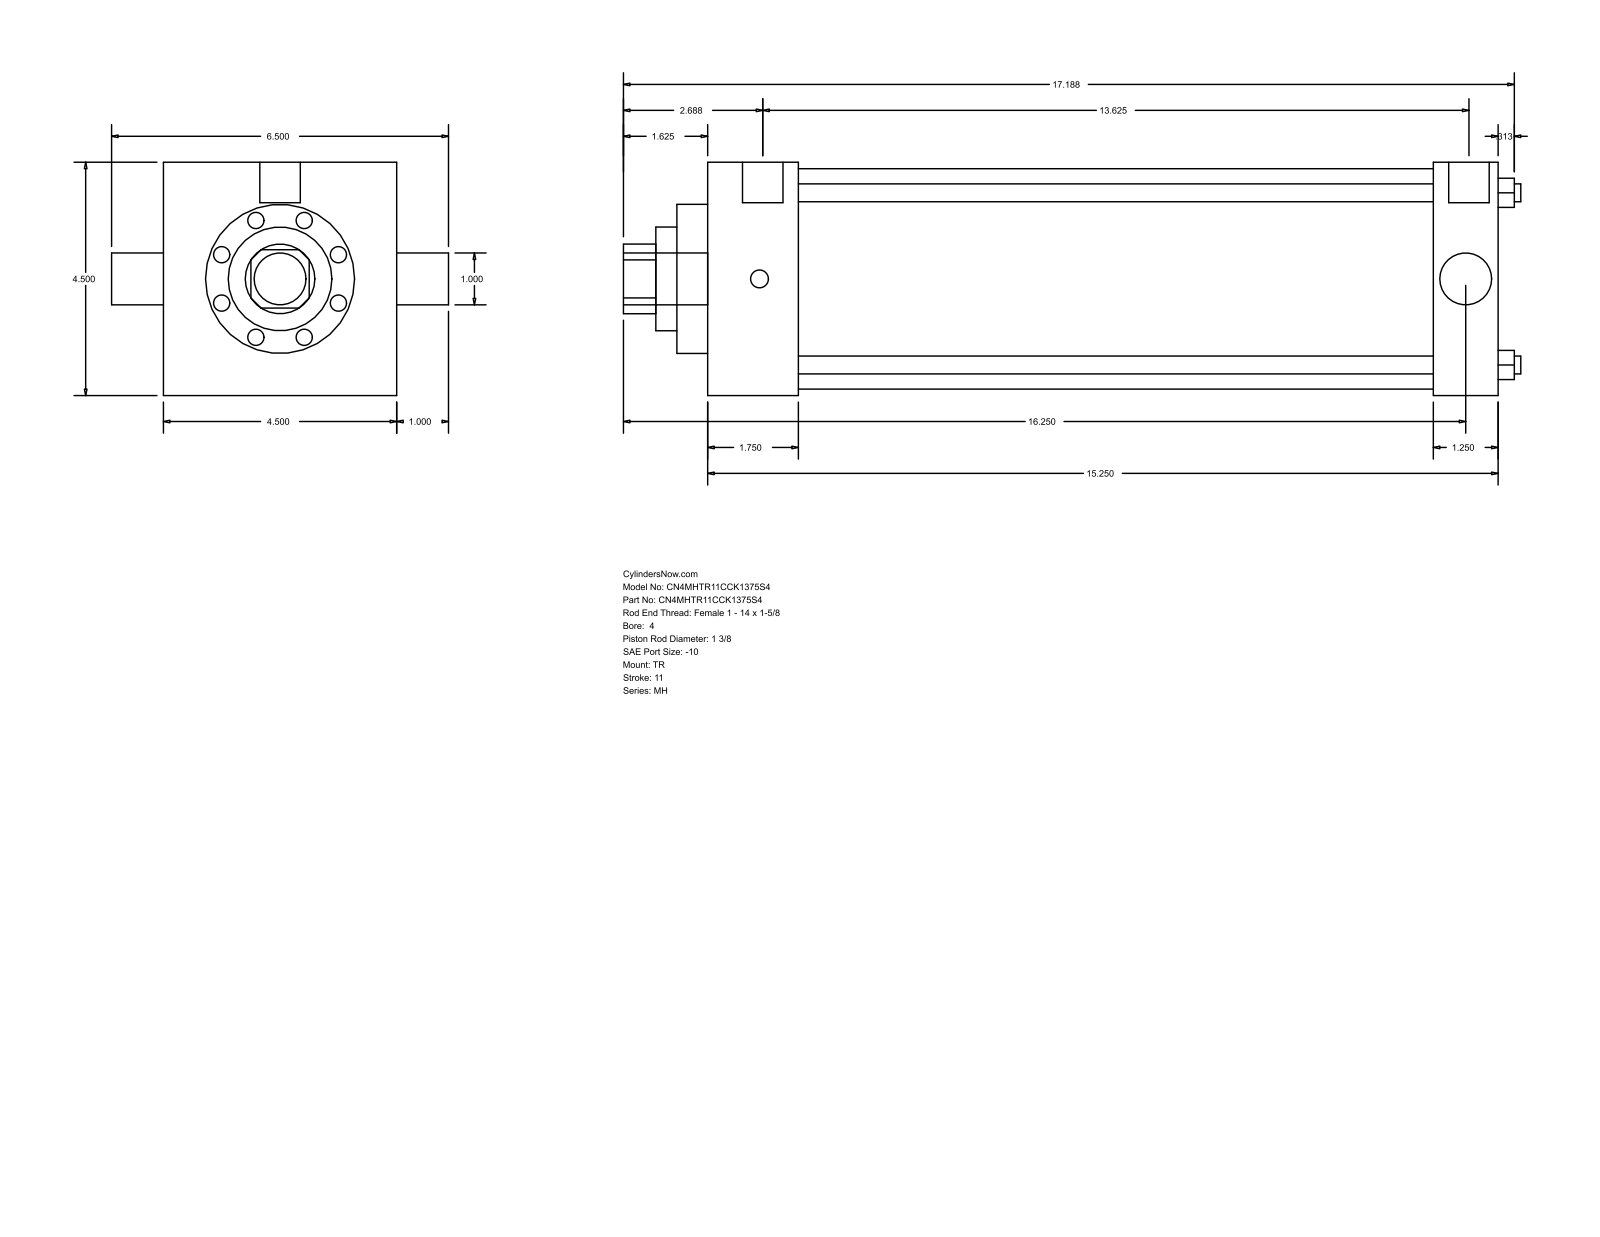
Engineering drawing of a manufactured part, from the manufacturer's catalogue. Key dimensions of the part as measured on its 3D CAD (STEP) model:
Part name (STEP PRODUCT): MH_TR__0400_1.375
STEP written by: GSSL Pune (CONFIG_CONTROL_DESIGN)
Units: millimetres
Bodies: 0 solids, 86 faces (61 planar, 25 cylindrical, 0 other)
Overall size (bounding box): 439.74 × 165.1 × 114.3
Round holes (diameter × count): ⌀8.76 ×4, ⌀25.4 ×1, ⌀34.92 ×1, ⌀50.8 ×1, ⌀73.03 ×1, ⌀107.95 ×1
Round bosses / shafts (diameter × count): ⌀8.73 ×3, ⌀19.84 ×2, ⌀25.4 ×1
Partial cylindrical surfaces — rounded edges, fillets, slot ends (radius × count): R17.06 ×1
Main face-to-face distances: 114.3, 387.35, 44.45, 342.9, 355.61, 311.16, 31.74, 15.08, 59.53, 370.69
Hole centre spacings: 59.62, 84.32, 119.25
